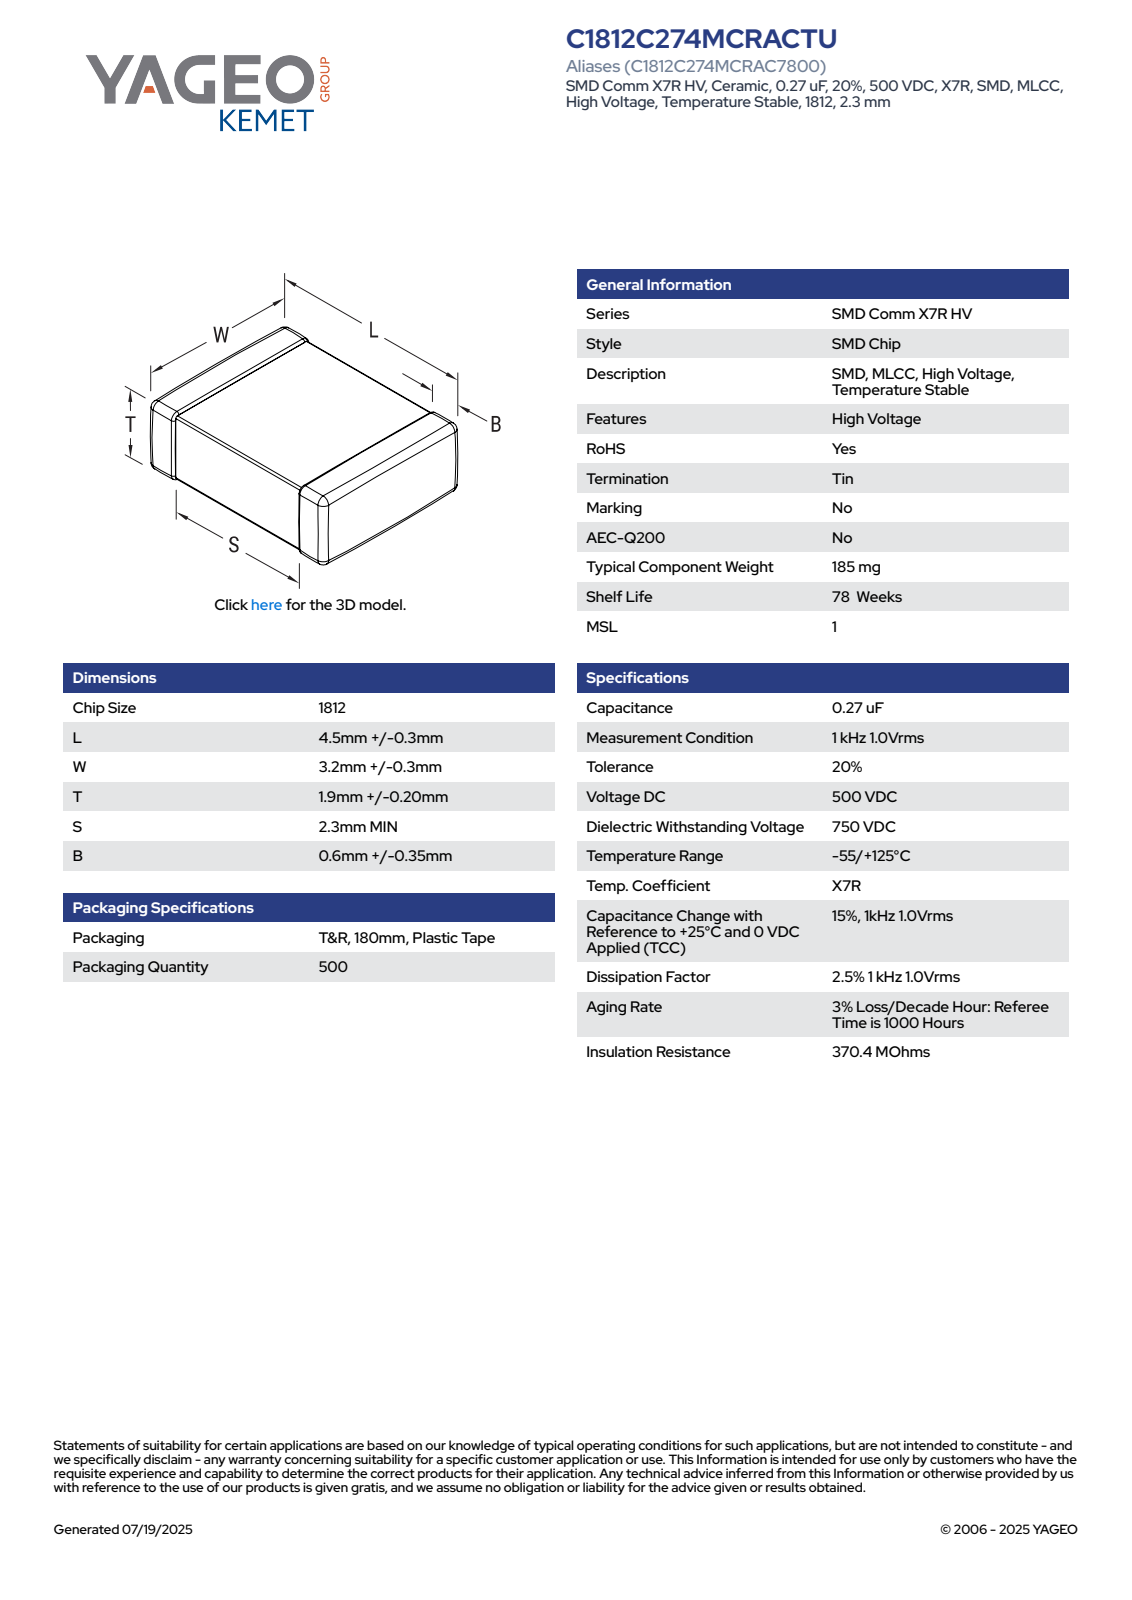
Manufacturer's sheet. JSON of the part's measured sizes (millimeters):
{"part_name": "CCS_CCSTD_1812_L4.8W3.5T2.1B0.6", "step_written_by": "SolidWorks 2021 (AUTOMOTIVE_DESIGN)", "units": "millimeters", "bodies": {"solids": 4, "faces": 129, "planar": 71, "cylindrical": 42, "other": 16}, "overall_size": [4.8, 3.5, 2.1], "volume_mm3": 33, "surface_area_mm2": 68, "face_to_face_distances": [2.03, 1.96, 4.8, 3.43, 2.1, 3.36, 3.5, 2.08, 2.72, 2.59]}
